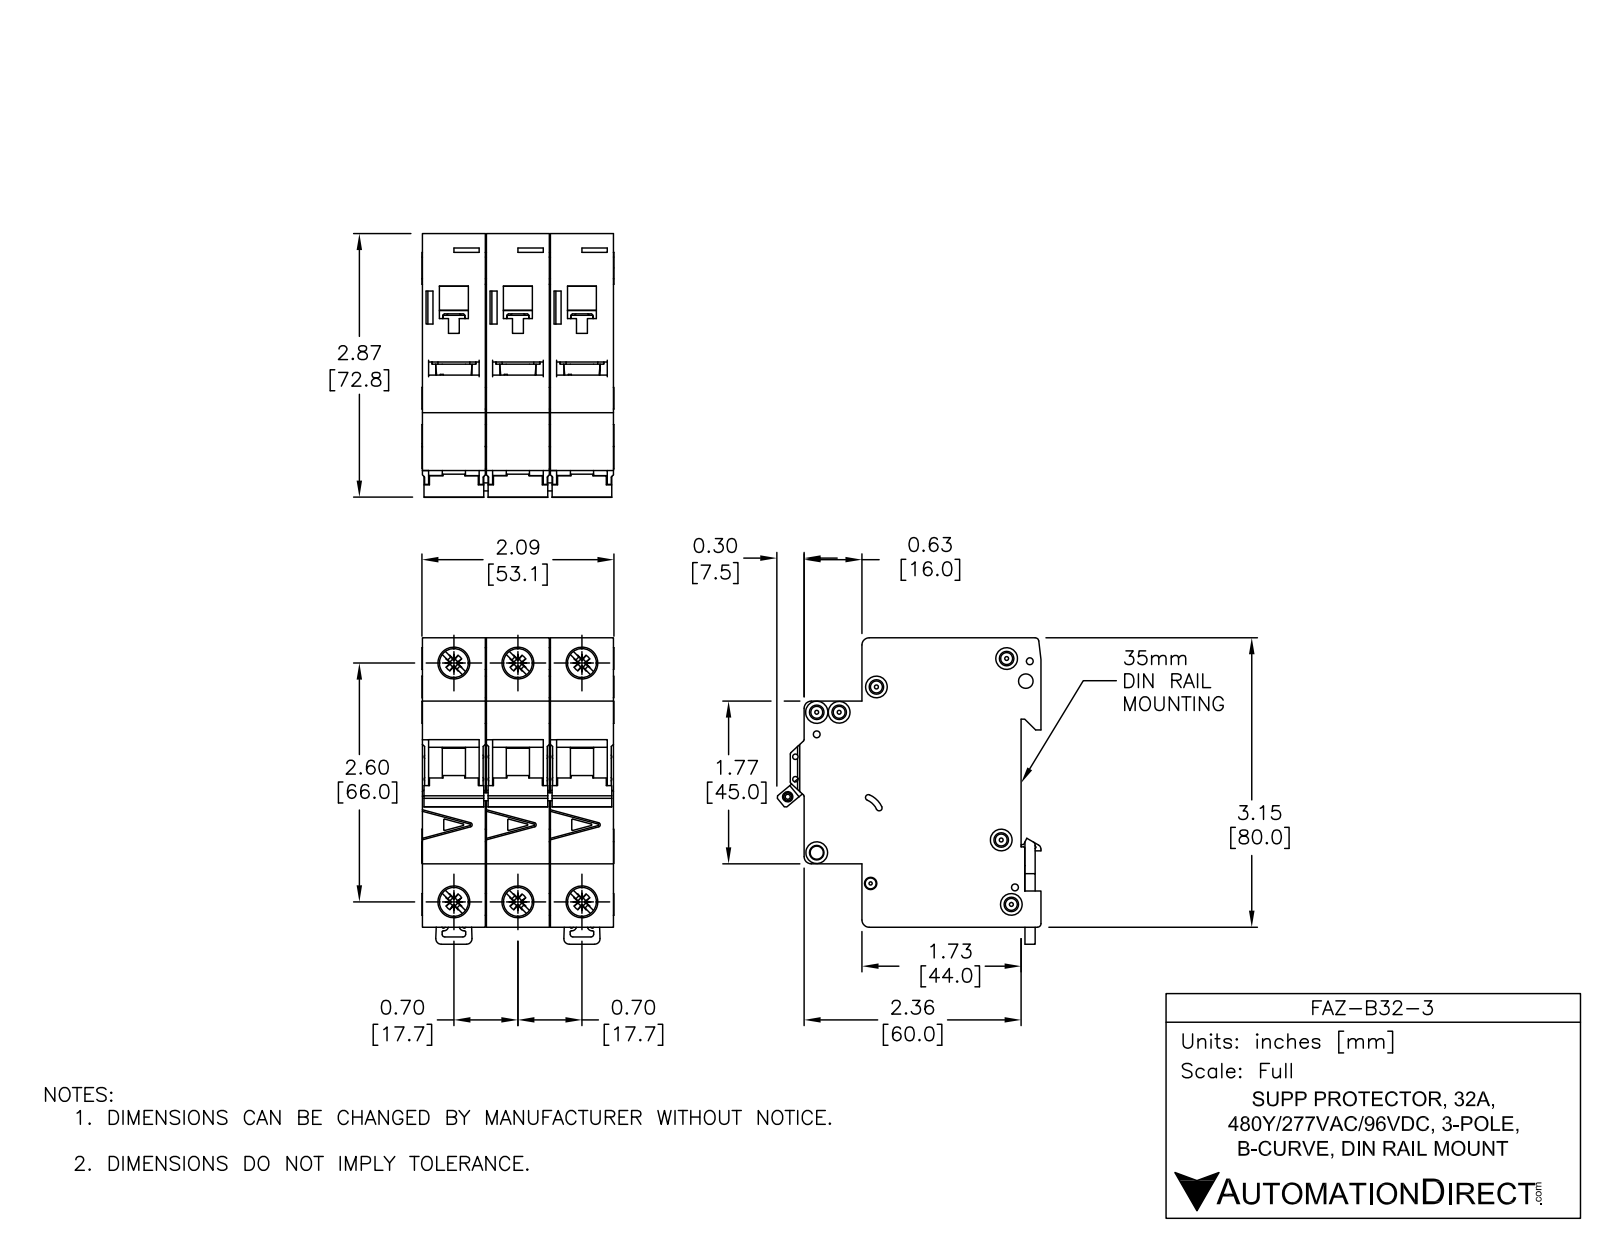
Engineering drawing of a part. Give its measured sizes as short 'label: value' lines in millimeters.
name: FAZ-B32-3
written by: SolidWorks 2014 (AUTOMOTIVE_DESIGN)
unit: mm
bodies: 11 solids, 1650 faces (697 planar, 590 cylindrical, 363 other)
size: 84.78 × 73.04 × 53.1
volume: 224 680 mm³; area: 58 052 mm²
holes: 6× ⌀3.6, 4× ⌀8.2, 3× ⌀1.9, 2× ⌀1.09, 2× ⌀1.5, 2× ⌀4, 2× ⌀7.15, 1× ⌀2.15, 1× ⌀2.2, 1× ⌀2.55, 1× ⌀3.3, 1× ⌀3.4
bosses: 4× ⌀6, 3× ⌀2.5, 2× ⌀8.2
rounds: 68× R0.25, 25× R0.5, 12× R1, 12× R2, 11× R0.2, 3× R1.8, 2× R0.8, 2× R3
face distances: 17.7, 17.5, 35.4, 35.2, 52.9, 17.9, 79.48, 5.5, 49.5, 44
hole spacings: 17.7, 68.33, 66, 6.2, 13.64, 35.4, 74.89, 4.81
